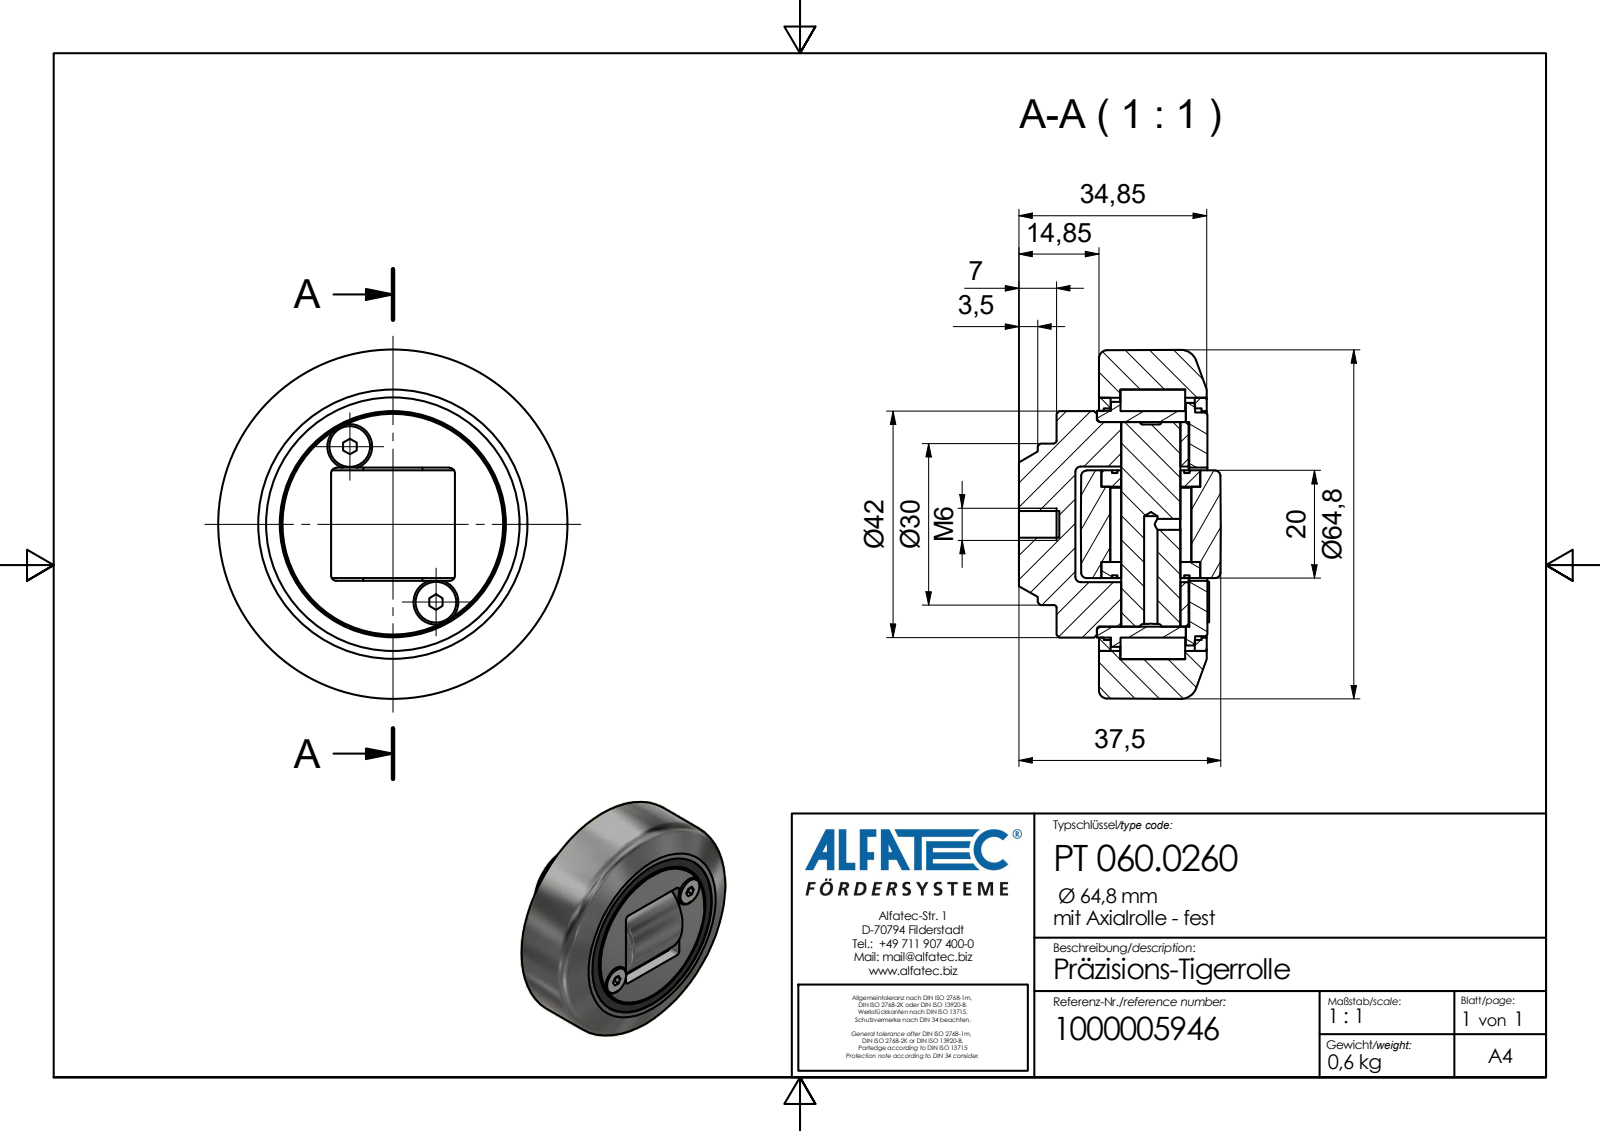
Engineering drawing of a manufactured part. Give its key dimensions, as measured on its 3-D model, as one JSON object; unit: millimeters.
{"part_name": "PT060.0260_Kontur", "step_written_by": "Autodesk Inventor 2020 (AP242_MANAGED_MODEL_BASED_3D_ENGINEERING_MIM_LF)", "units": "millimeters", "bodies": {"solids": 2, "faces": 140, "planar": 53, "cylindrical": 50, "other": 37}, "overall_size": [64.8, 64.8, 37.5], "volume_mm3": 66659, "surface_area_mm2": 27713, "round_holes": [[2.5, 2], [4.3, 2], [2, 1], [3, 1], [4.92, 1], [15, 1], [18.4, 1], [38, 1], [42, 1], [42.97, 1], [47, 1], [50, 1]], "round_bosses_or_shafts": [[7.53, 2], [4, 2], [45.5, 1], [45, 1], [42.1, 1], [41.5, 1], [37, 1], [30, 1]], "partial_cylinders_radius": [[1, 8], [1.35, 2], [1.5, 1], [14, 1]], "face_to_face_distances": [3.35, 28, 3.5, 20.15, 20, 16.8, 0.75, 7.85, 24.65, 27.85], "hole_center_spacings": [16.5, 33]}
